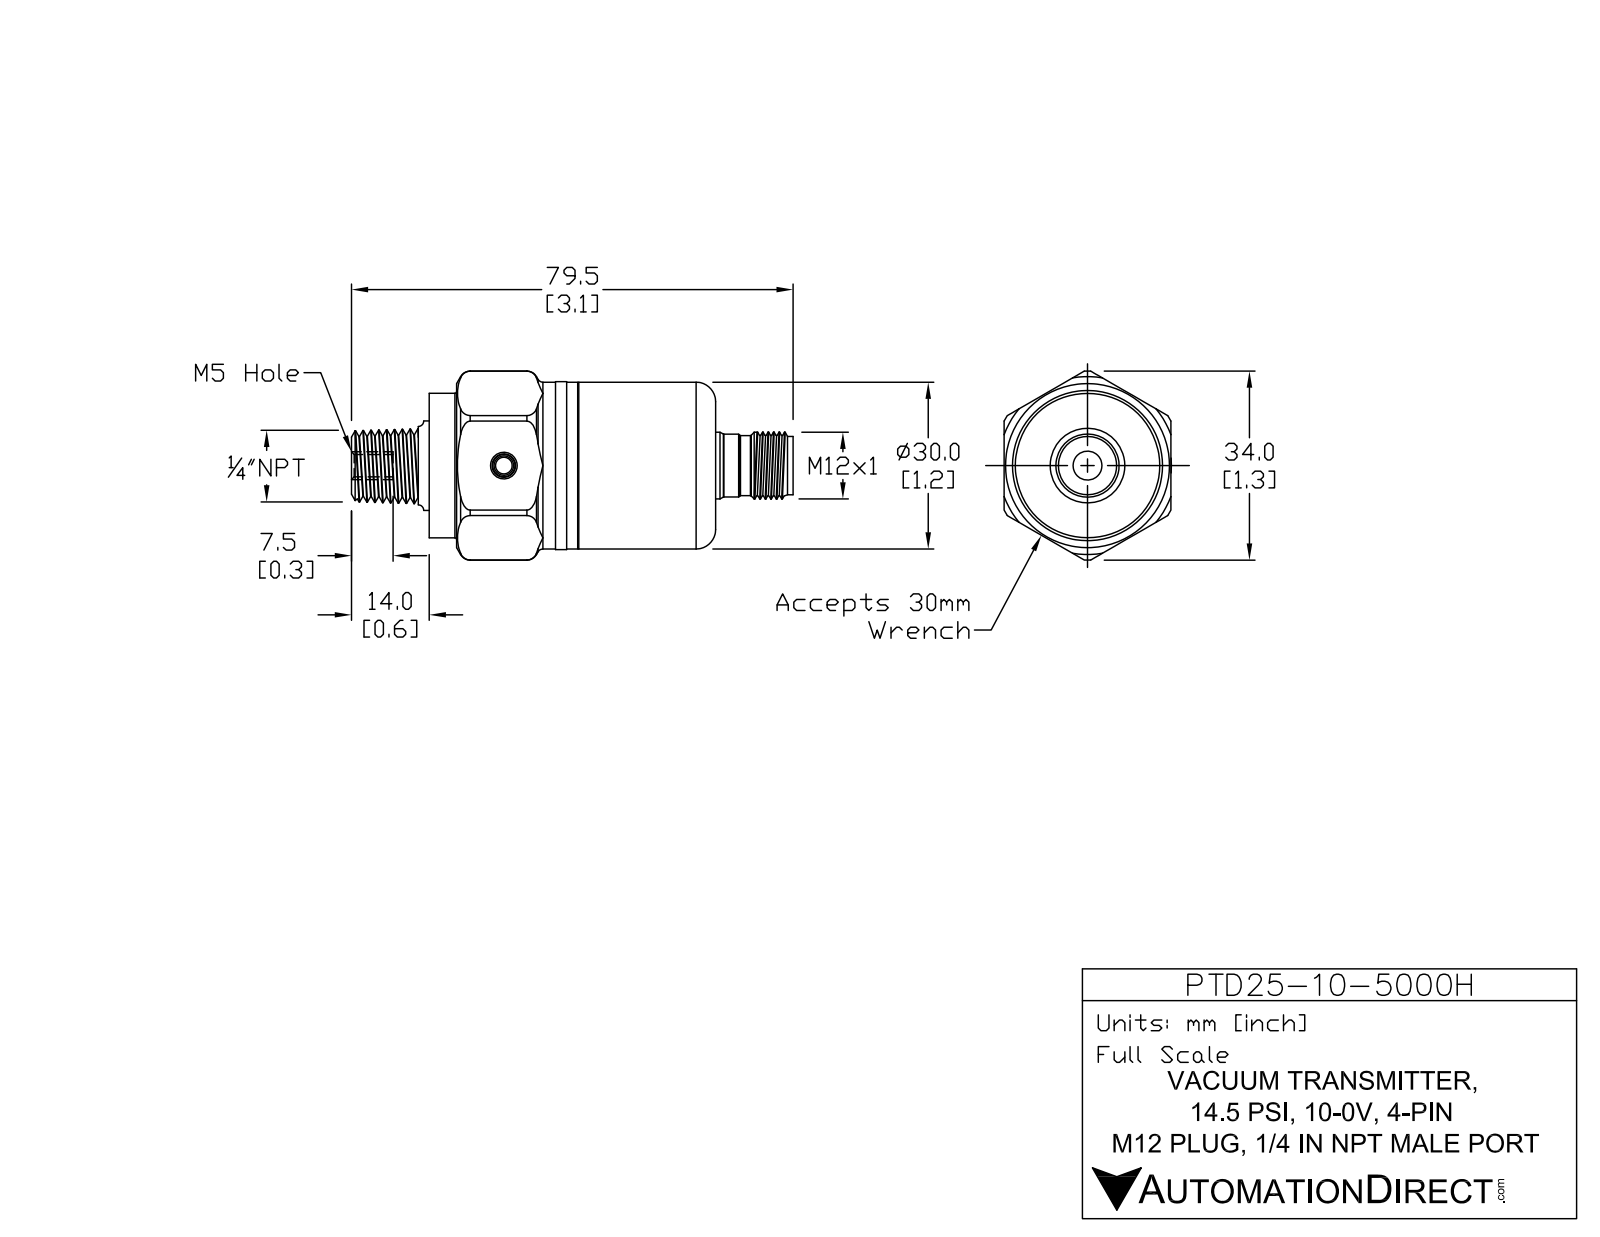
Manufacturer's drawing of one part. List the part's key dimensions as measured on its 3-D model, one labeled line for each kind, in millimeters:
Part name (STEP PRODUCT): PTD25-10-VH
STEP written by: SolidWorks 2017 (AUTOMOTIVE_DESIGN)
Units: millimetres
Bodies: 1 solid, 124 faces (36 planar, 59 cylindrical, 29 other)
Overall size (bounding box): 79.5 × 33.78 × 31.7
Volume: 39 212 mm³ · Surface area: 8 088 mm²
Round holes (diameter × count): ⌀4 ×1, ⌀8.5 ×1
Round bosses / shafts (diameter × count): ⌀30.05 ×1, ⌀30 ×1, ⌀25.96 ×1, ⌀14 ×1, ⌀13.5 ×1, ⌀12 ×1
Partial cylindrical surfaces — rounded edges, fillets, slot ends (radius × count): R3.76 ×1, R16.95 ×1
Main face-to-face distances: 51, 29.98, 30, 48, 3, 65, 17, 14, 30.01, 5.65
